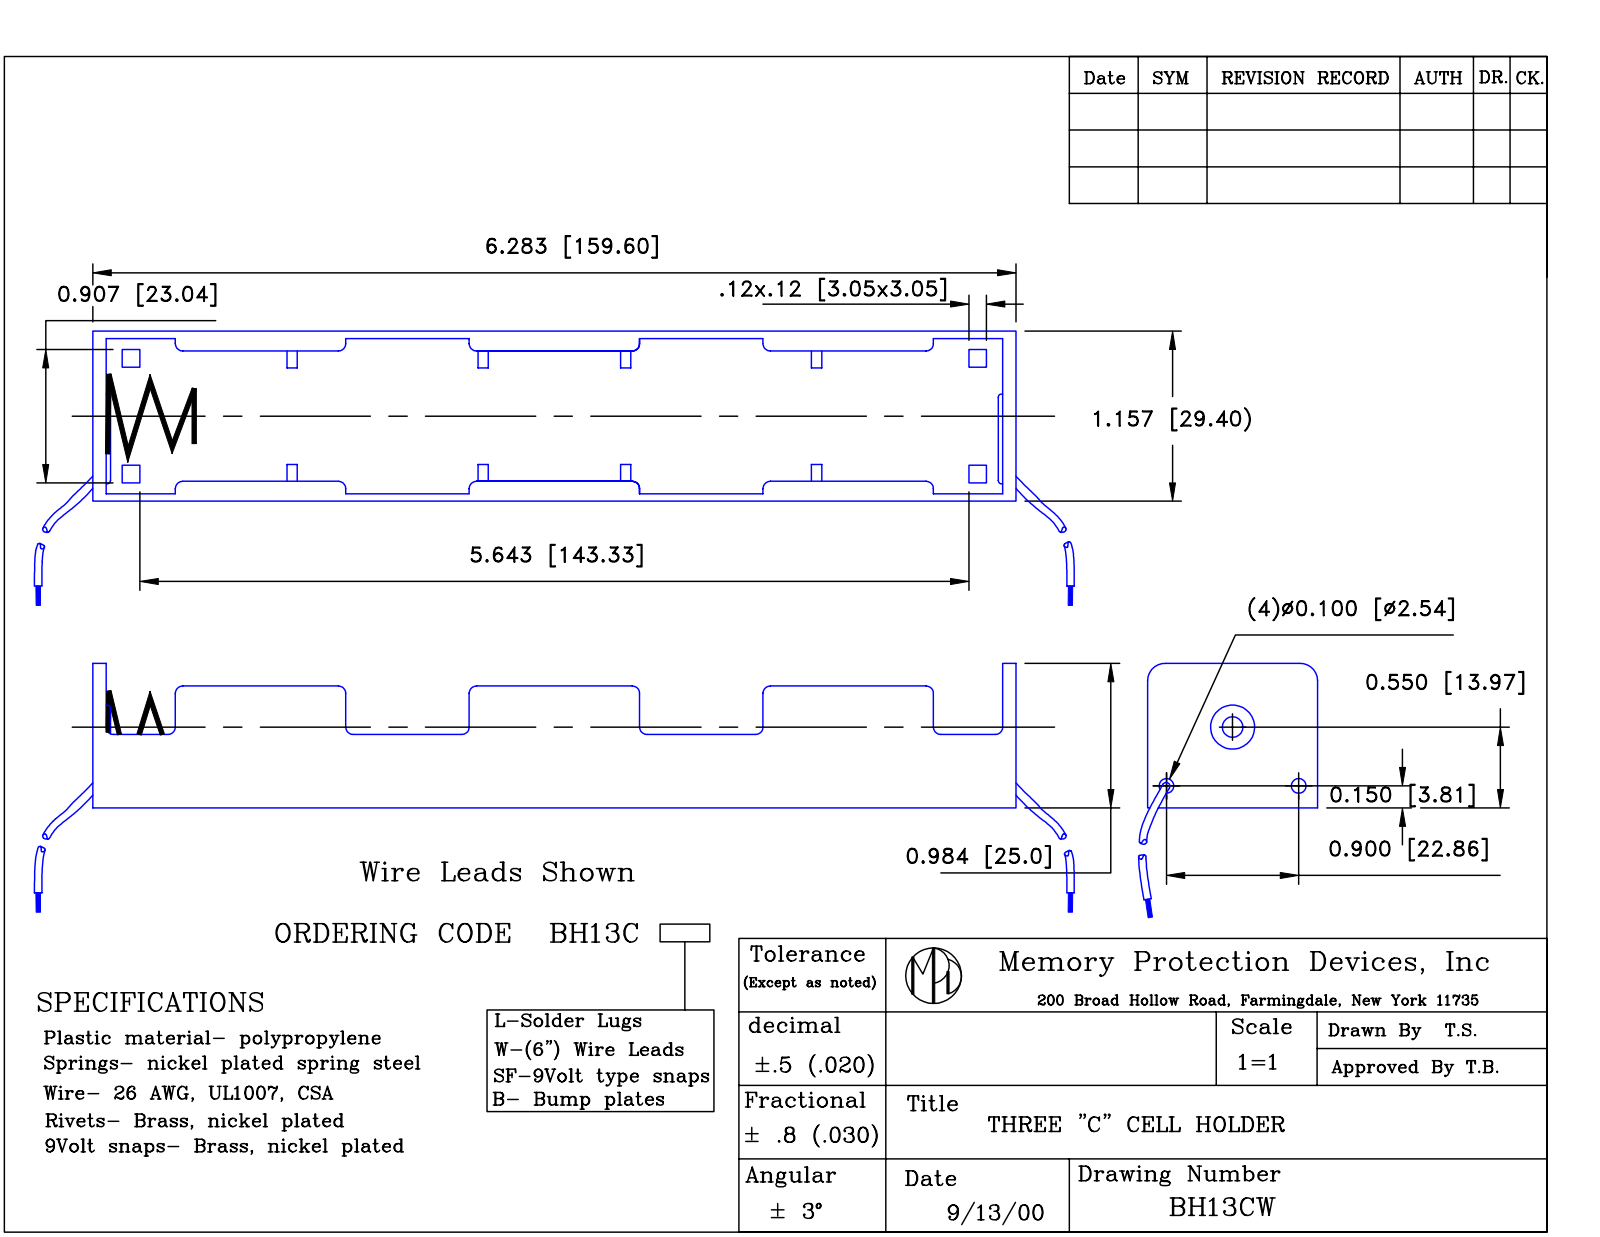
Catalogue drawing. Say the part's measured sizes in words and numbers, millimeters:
The part is named "BH13CW". Its 3-D file was written by "SolidWorks 2017 (AUTOMOTIVE_DESIGN)". It is 7 solids with 223 faces: 111 planar, 82 cylindrical and 30 other. Overall it measures 459.6 by 29.4 by 25 millimeters. Its volume is 19 460 cubic millimeters and its surface area 25 237 square millimeters. Round holes: 2 of diameter 2.54, 1 of diameter 0.4, 1 of diameter 1.6, 1 of diameter 2.3, 1 of diameter 3, 1 of diameter 8. Round bosses or shafts: 1 of diameter 6.2, 1 of diameter 3.5, 1 of diameter 0.81, 1 of diameter 0.6. Partial cylindrical surfaces (rounded edges, fillets, slot ends): 12 of radius 3, 2 of radius 5, 2 of radius 7.61, 2 of radius 7.96. The main face-to-face distances are 1.6, 2, 27.8, 29.4, 26.2, 158, 156.4, 159.6, 12, 10. The hole center spacings are 16.15, 23.2.
